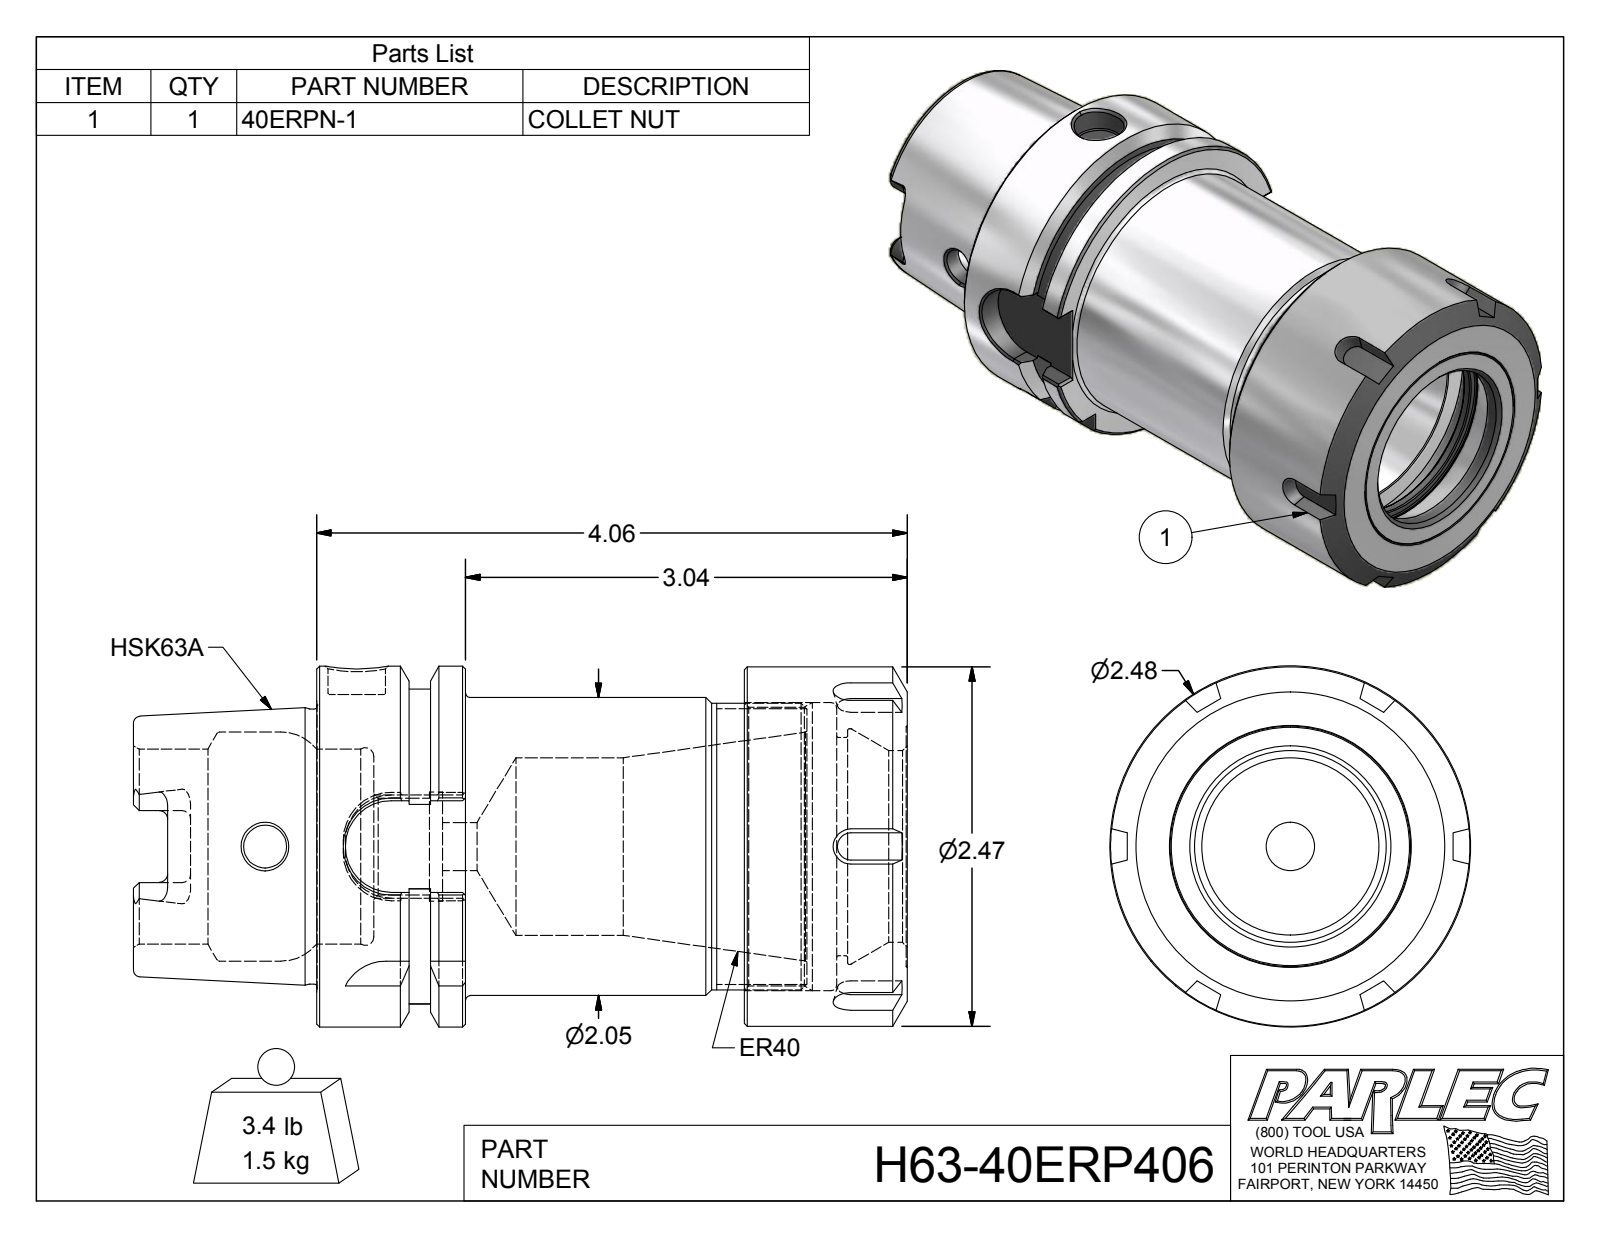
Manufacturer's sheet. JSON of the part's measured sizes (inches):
{"part_name": "H63-40ERP406; H63-40ER4-1; 40ERPN", "step_written_by": "Autodesk Inventor 2012 (AUTOMOTIVE_DESIGN)", "units": "inches", "bodies": {"solids": 2, "faces": 190, "planar": 79, "cylindrical": 42, "other": 69}, "overall_size": [5.32, 2.48, 2.48], "volume_in3": 12.12, "surface_area_in2": 78.63, "round_holes": [[0.295, 1], [0.331, 1], [0.394, 1], [0.666, 1], [0.749, 1], [1.22, 1], [1.318, 1], [1.339, 1], [1.5, 1], [1.575, 1], [1.62, 1], [1.916, 1]], "round_bosses_or_shafts": [[2.48, 1], [2.47, 1], [2.047, 1], [1.969, 1], [1.891, 1]], "partial_cylinders_radius": [[0.059, 6], [0.113, 4], [0.315, 4], [1.083, 1]], "face_to_face_distances": [1.12, 2.94, 4.06, 1.024, 3.576, 0.636, 0.484, 0.241, 0.389, 1.917]}
